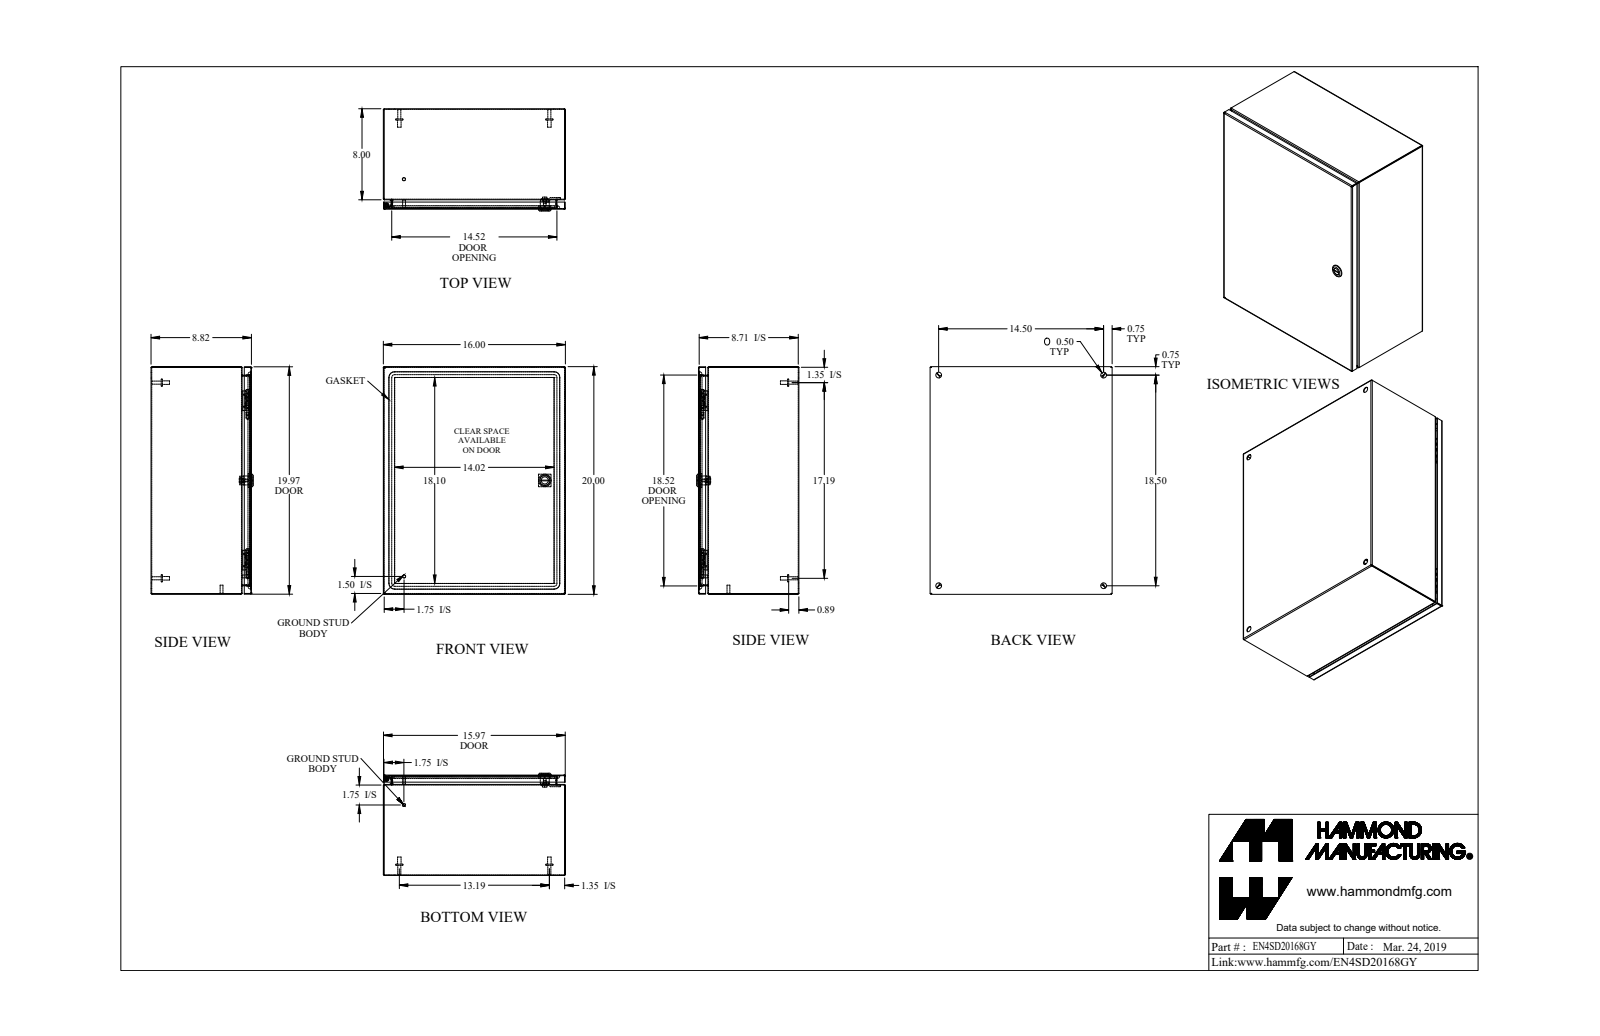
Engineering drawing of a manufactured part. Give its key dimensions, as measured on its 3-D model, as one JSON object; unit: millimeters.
{"part_name": "EN4SD20168GY_Default", "step_written_by": "SolidWorks 2019 (CONFIG_CONTROL_DESIGN)", "units": "millimeters", "bodies": {"solids": 21, "faces": 634, "planar": 285, "cylindrical": 213, "other": 136}, "overall_size": [508, 406.4, 228.1], "volume_mm3": 1384000, "surface_area_mm2": 1853000, "round_holes": [[12.7, 4], [4.4, 1], [5.9, 1], [6.1, 1], [6.1, 1], [15.9, 1], [19.9, 1]], "round_bosses_or_shafts": [[15.9, 4], [8, 4], [6.9, 4], [7.1, 2], [6.4, 2], [27.9, 1], [13.3, 1], [11.6, 1]], "partial_cylinders_radius": [[0.7, 21], [2.2, 21], [6.4, 16], [482.6, 8], [0.2, 4], [1.6, 4], [12.7, 4], [3.2, 2]], "face_to_face_distances": [1.4, 222.6, 221.2, 224.1, 405, 506.6, 403.5, 406.4, 505.1, 508], "hole_center_spacings": [368.3, 469.9, 597.1, 236.5, 236.5, 414.4, 414.5]}
